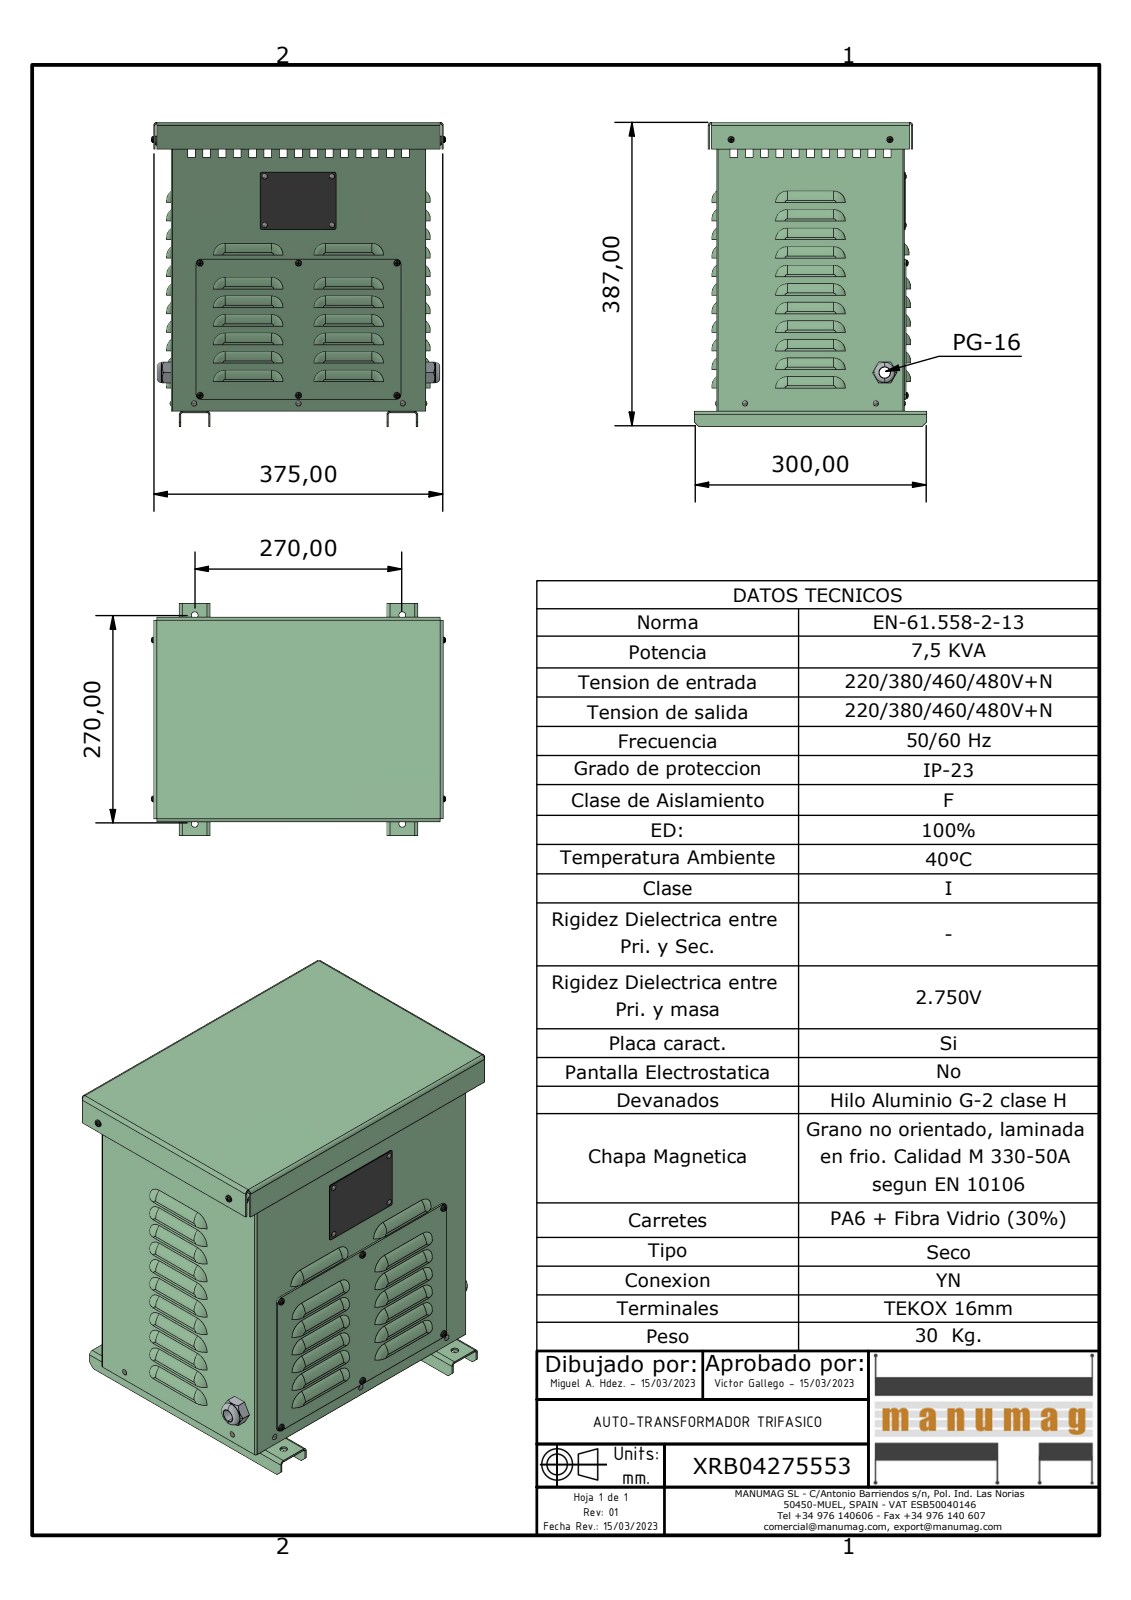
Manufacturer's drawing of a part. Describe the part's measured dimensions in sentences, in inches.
The part is named "XRB04275553; JE010 EXPORT BASE; JE010 EXPORT PATA; JE010 EXPORT CUERPO (+6 more)". Its 3-D file was written by "Autodesk Inventor 2023 (AUTOMOTIVE_DESIGN)". It is 33 solids with 1975 faces: 1082 planar, 421 cylindrical and 472 other. Overall it measures 15.513 by 15.006 by 11.811 inches. Its volume is 105 cubic inches and its surface area 2 351 square inches. Round holes: 8 of diameter 0.091, 8 of diameter 0.146, 8 of diameter 0.346, 5 of diameter 0.169, 4 of diameter 0.134, 4 of diameter 0.157, 3 of diameter 0.197, 1 of diameter 0.551, 1 of diameter 0.945. Round bosses or shafts: 9 of diameter 0.126, 8 of diameter 0.157, 8 of diameter 0.143, 1 of diameter 1.024, 1 of diameter 0.906, 1 of diameter 0.886. Partial cylindrical surfaces (rounded edges, fillets, slot ends): 105 of radius 0.551, 68 of radius 0.157, 40 of radius 0.591, 20 of radius 0.079, 6 of radius 0.059, 5 of radius 0.079, 4 of radius 0.236. The main face-to-face distances are 0.079, 9.473, 12.887, 14.646, 9.552, 14.725, 9.394, 12.808, 12.965, 0.157. The hole center spacings are 2.204, 5.012, 6.649, 8.269, 8.394, 8.398, 13.498, 2.48.
